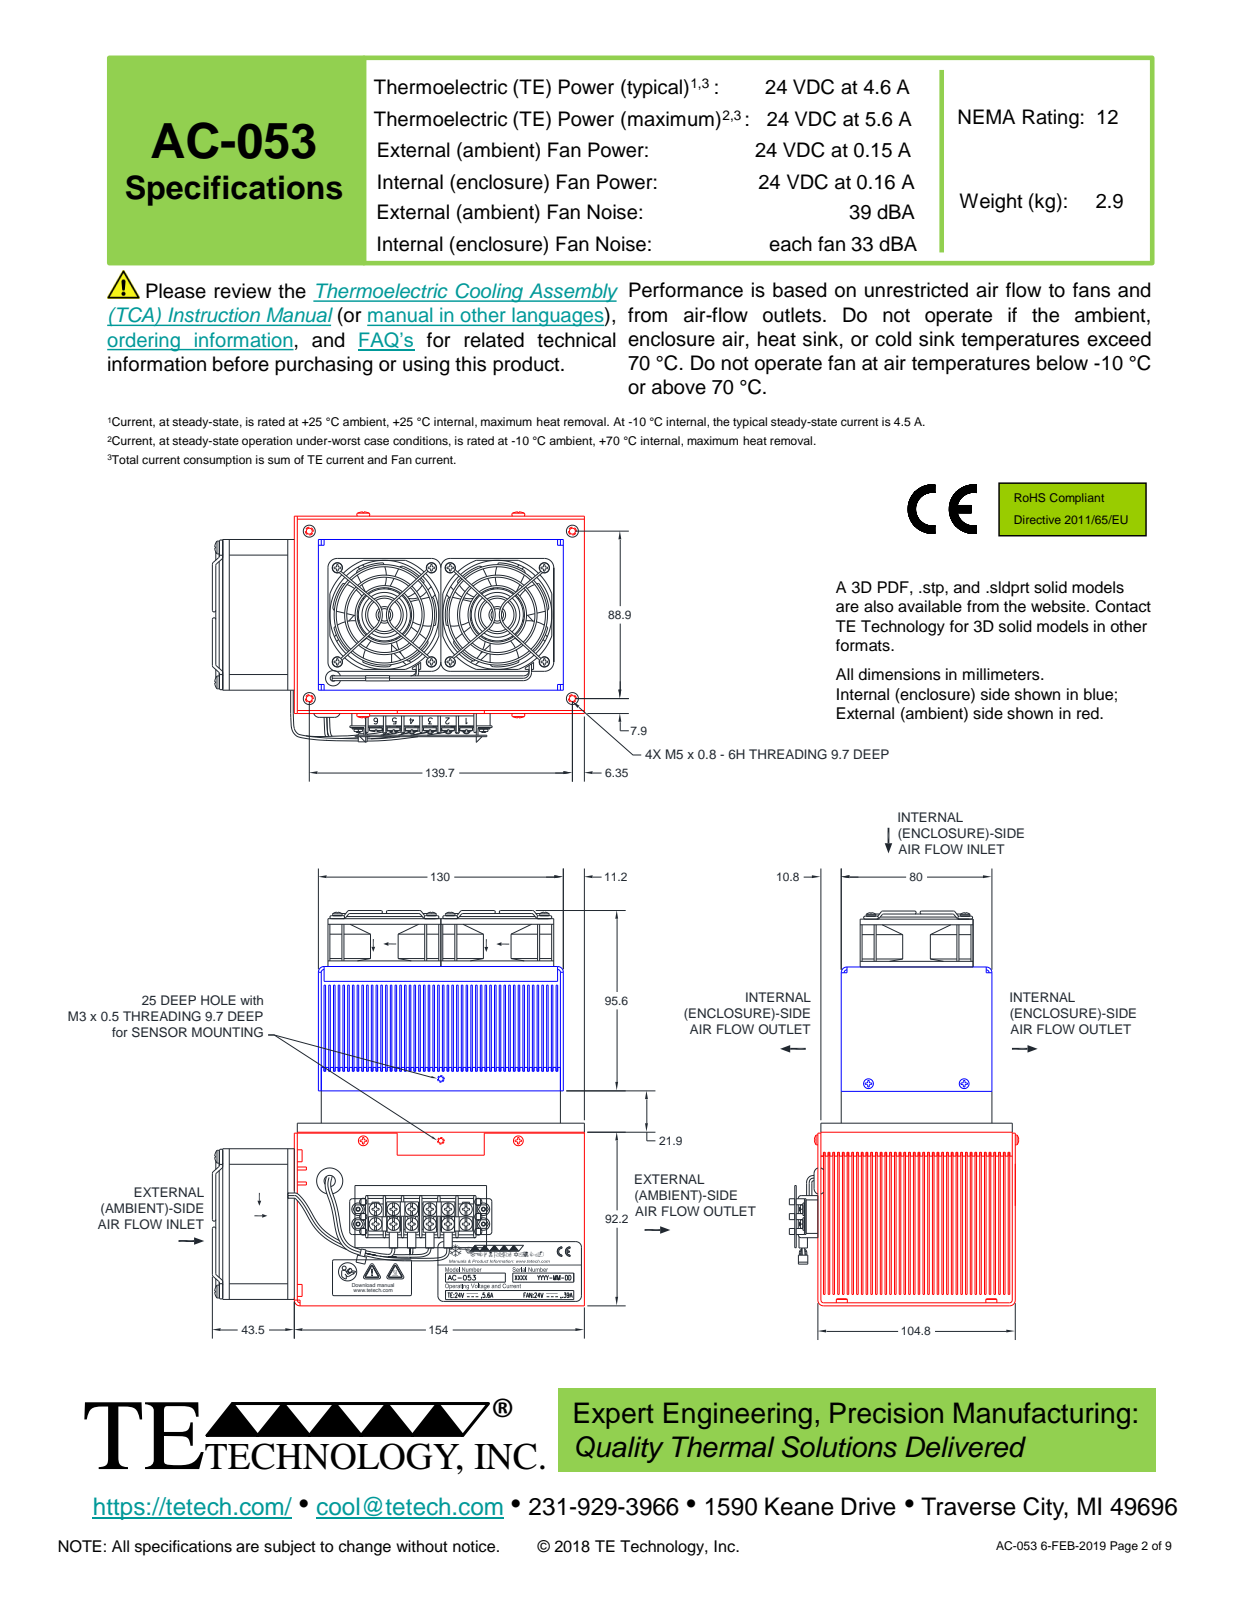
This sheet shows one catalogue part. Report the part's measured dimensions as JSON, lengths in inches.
{"part_name": "AC-053 gasket; 6-32pph x .38; 4-40-flat-head; AC-053 heat sink gasket (+8 more)", "step_written_by": "Alibre (AUTOMOTIVE_DESIGN)", "units": "inches", "bodies": {"solids": 202, "faces": 5908, "planar": 2997, "cylindrical": 1137, "other": 1774}, "overall_size": [8.266, 7.776, 4.818], "volume_in3": 77.04, "surface_area_in2": 2281, "round_holes": [[0.104, 17], [0.219, 15], [0.104, 12], [0.166, 11], [0.25, 9], [0.163, 8], [0.169, 8], [0.075, 6], [0.139, 6], [0.155, 6], [0.17, 6], [0.067, 4]], "round_bosses_or_shafts": [[0.056, 36], [0.138, 29], [0.27, 26], [0.063, 23], [0.072, 15], [0.25, 12], [0.071, 9], [0.313, 8]], "partial_cylinders_radius": [[0.02, 68], [0.008, 36], [0.024, 30], [0.031, 24], [0.039, 23], [0.038, 21], [0.012, 18], [0.906, 14]], "face_to_face_distances": [0.198, 0.396, 0.099, 0.297, 0.099, 0.495, 0.594, 0.693, 0.063, 0.23], "hole_center_spacings": [0.31, 0.75, 0.811, 1.969, 0.375, 0.487, 2.369, 0.372]}
